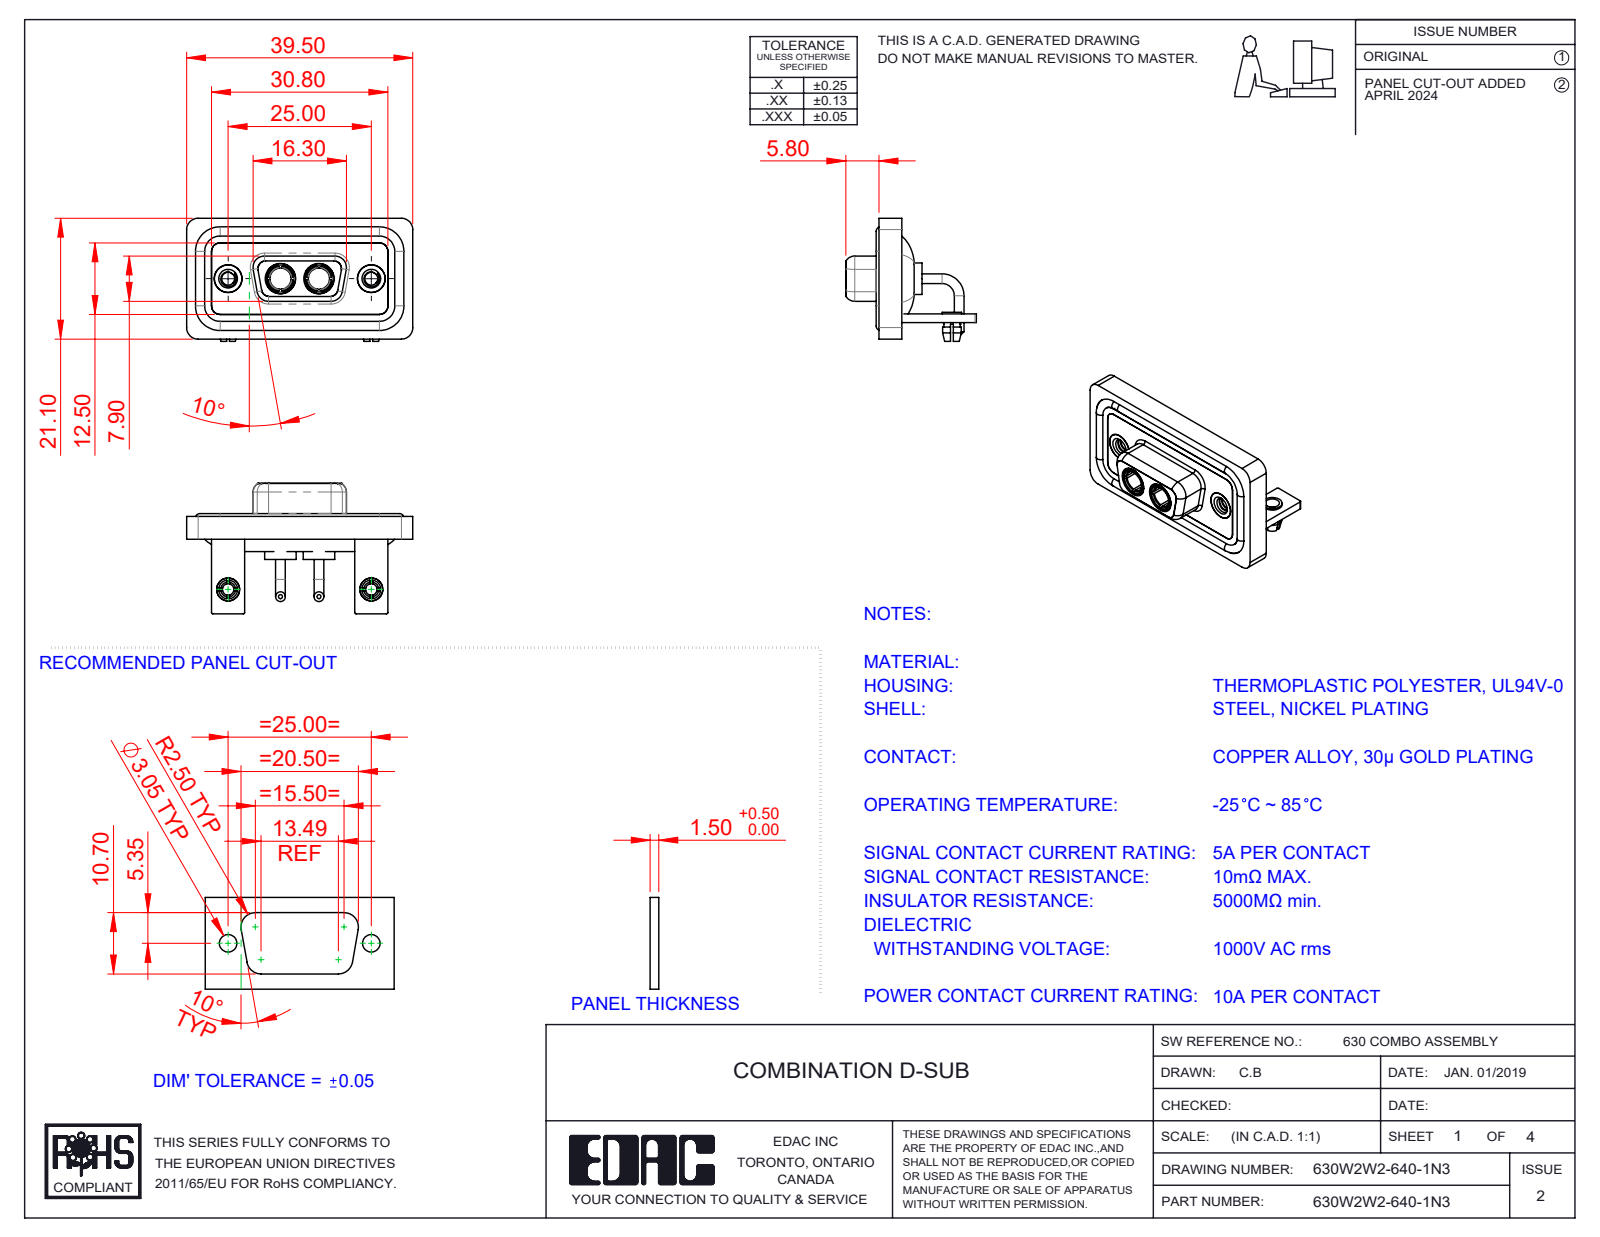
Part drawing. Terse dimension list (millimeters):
name: 630Combo Threaded Rivet_2; 630Combo Shell Front_09 Contacts; 630Combo Housing_2W2; 630Combo Shell Rear_09 Contacts (+5 more)
written by: SolidWorks 2023 (CONFIG_CONTROL_DESIGN)
unit: mm
bodies: 15 solids, 682 faces (231 planar, 294 cylindrical, 157 other)
size: 39.5 × 22.8 × 21.5
volume: 5 103 mm³; area: 8 630 mm²
holes: 4× ⌀4.85, 2× ⌀2, 2× ⌀2.26, 2× ⌀2.5, 2× ⌀3.2, 2× ⌀3.7, 2× ⌀4, 2× ⌀4.05, 2× ⌀5, 2× ⌀5.3
bosses: 4× ⌀1.7, 4× ⌀1.6, 2× ⌀5.5, 2× ⌀5.2, 2× ⌀4.96, 2× ⌀4.95, 2× ⌀4.8, 2× ⌀4.75
rounds: 19× R2, 18× R1.5, 16× R0.25, 8× R1.35, 8× R1.6, 5× R0.5, 4× R0.6, 4× R0.65
face distances: 0.4, 2.9, 1.5, 1.8, 1.1, 3.7, 0.8, 2.5, 1.6, 3.1
hole spacings: 9.14, 15.86, 25, 6.72
